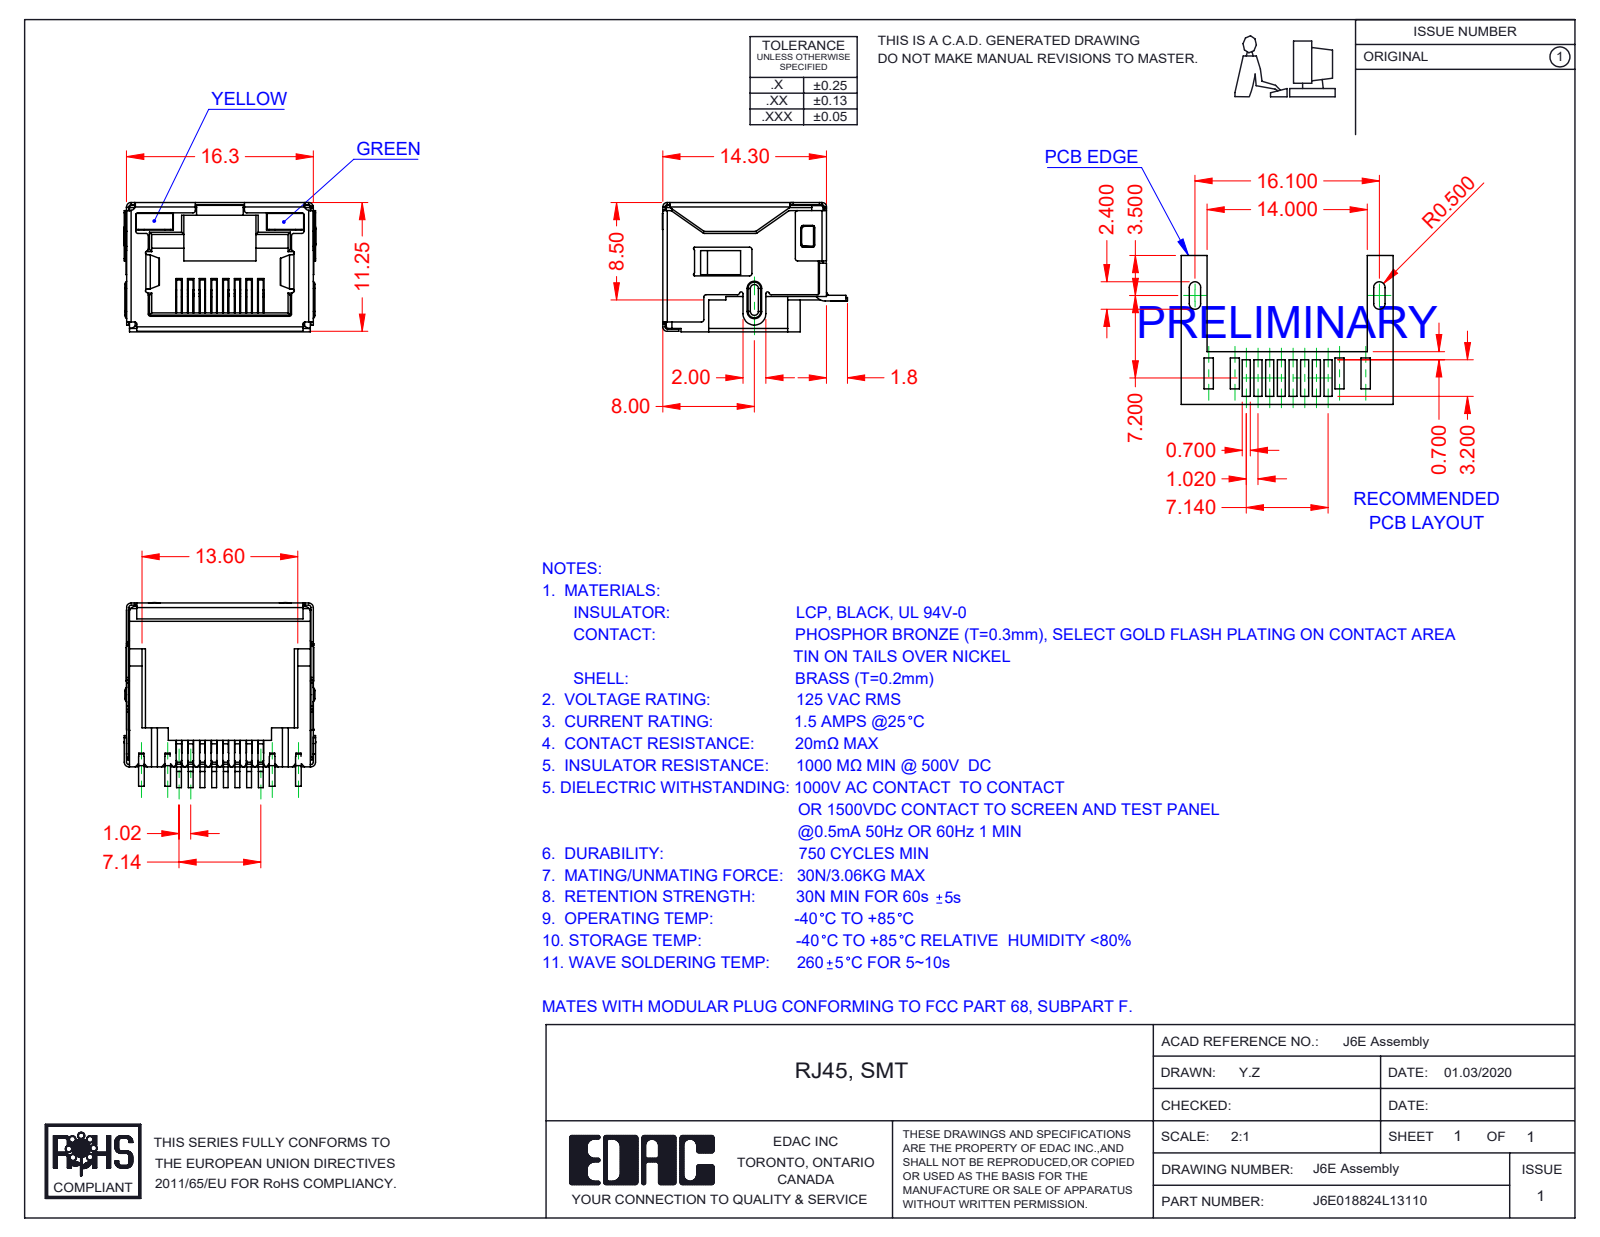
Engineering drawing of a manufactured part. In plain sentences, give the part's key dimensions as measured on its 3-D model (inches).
The part is named "J6E018824L13110; 6E Insulator_LED; 6E LED LH_1-Yellow; 6E LED RH_3-Green (+2 more)". Its 3-D file was written by "SolidWorks 2016 (CONFIG_CONTROL_DESIGN)". It is 12 solids with 1496 faces: 1099 planar, 347 cylindrical and 50 other. Overall it measures 0.659 by 0.636 by 0.445 inches. Its volume is 0.068 cubic inches and its surface area 6.27 square inches. Partial cylindrical surfaces (rounded edges, fillets, slot ends): 82 of radius 0.008, 17 of radius 0.01, 13 of radius 0.016, 13 of radius 0.02, 10 of radius 0.004, 7 of radius 0.006, 4 of radius 0.012, 3 of radius 0.039. The main face-to-face distances are 0.435, 0.632, 0.634, 0.624, 0.437, 0.445, 0.094, 0.028, 0.388, 0.019.
